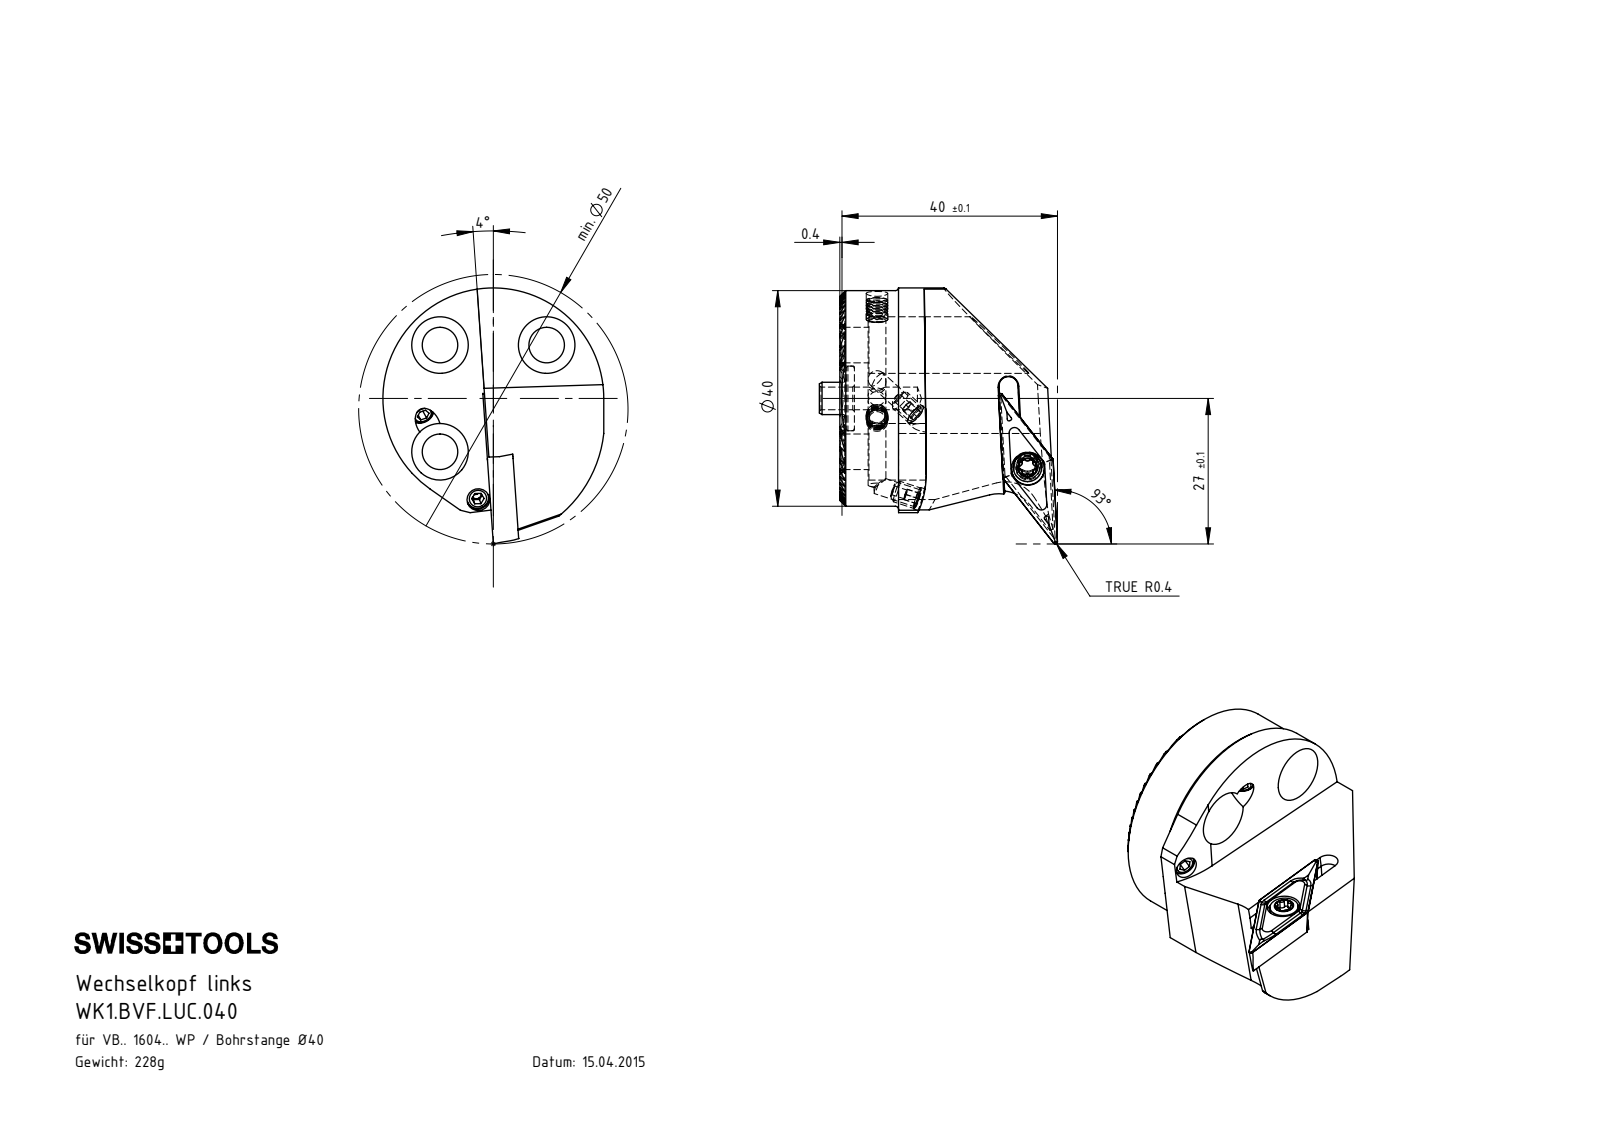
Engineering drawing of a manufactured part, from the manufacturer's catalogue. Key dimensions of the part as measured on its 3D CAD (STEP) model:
Part name (STEP PRODUCT): WK1.BVF.LUC.040; WKX-ER1.004.005_A_PreviewCfg; KVT_MB_600_040; WK1-BVF.LUC.040_A (+3 more)
STEP written by: SolidWorks 2017 (AUTOMOTIVE_DESIGN)
Units: millimetres
Bodies: 10 solids, 566 faces (219 planar, 199 cylindrical, 148 other)
Overall size (bounding box): 47.5 × 44.2 × 41
Volume: 28 519 mm³ · Surface area: 11 800 mm²
Round holes (diameter × count): ⌀3.3 ×5, ⌀4.2 ×3, ⌀6.6 ×3, ⌀10.5 ×3, ⌀1.7 ×2, ⌀3 ×2, ⌀4 ×1, ⌀4.4 ×1, ⌀6.1 ×1, ⌀12 ×1
Round bosses / shafts (diameter × count): ⌀4 ×5, ⌀40 ×1, ⌀6 ×1, ⌀5.25 ×1
Partial cylindrical surfaces — rounded edges, fillets, slot ends (radius × count): R0.12 ×26, R0.34 ×6, R0.59 ×6, R0.15 ×2, R1.75 ×1, R7 ×1, R20 ×1, R20.5 ×1
Main face-to-face distances: 1.3, 2.6, 3.9, 12.99, 5.2, 11.69, 9.09, 10.39, 7.79, 6.5
Hole centre spacings: 14, 19.8, 28
